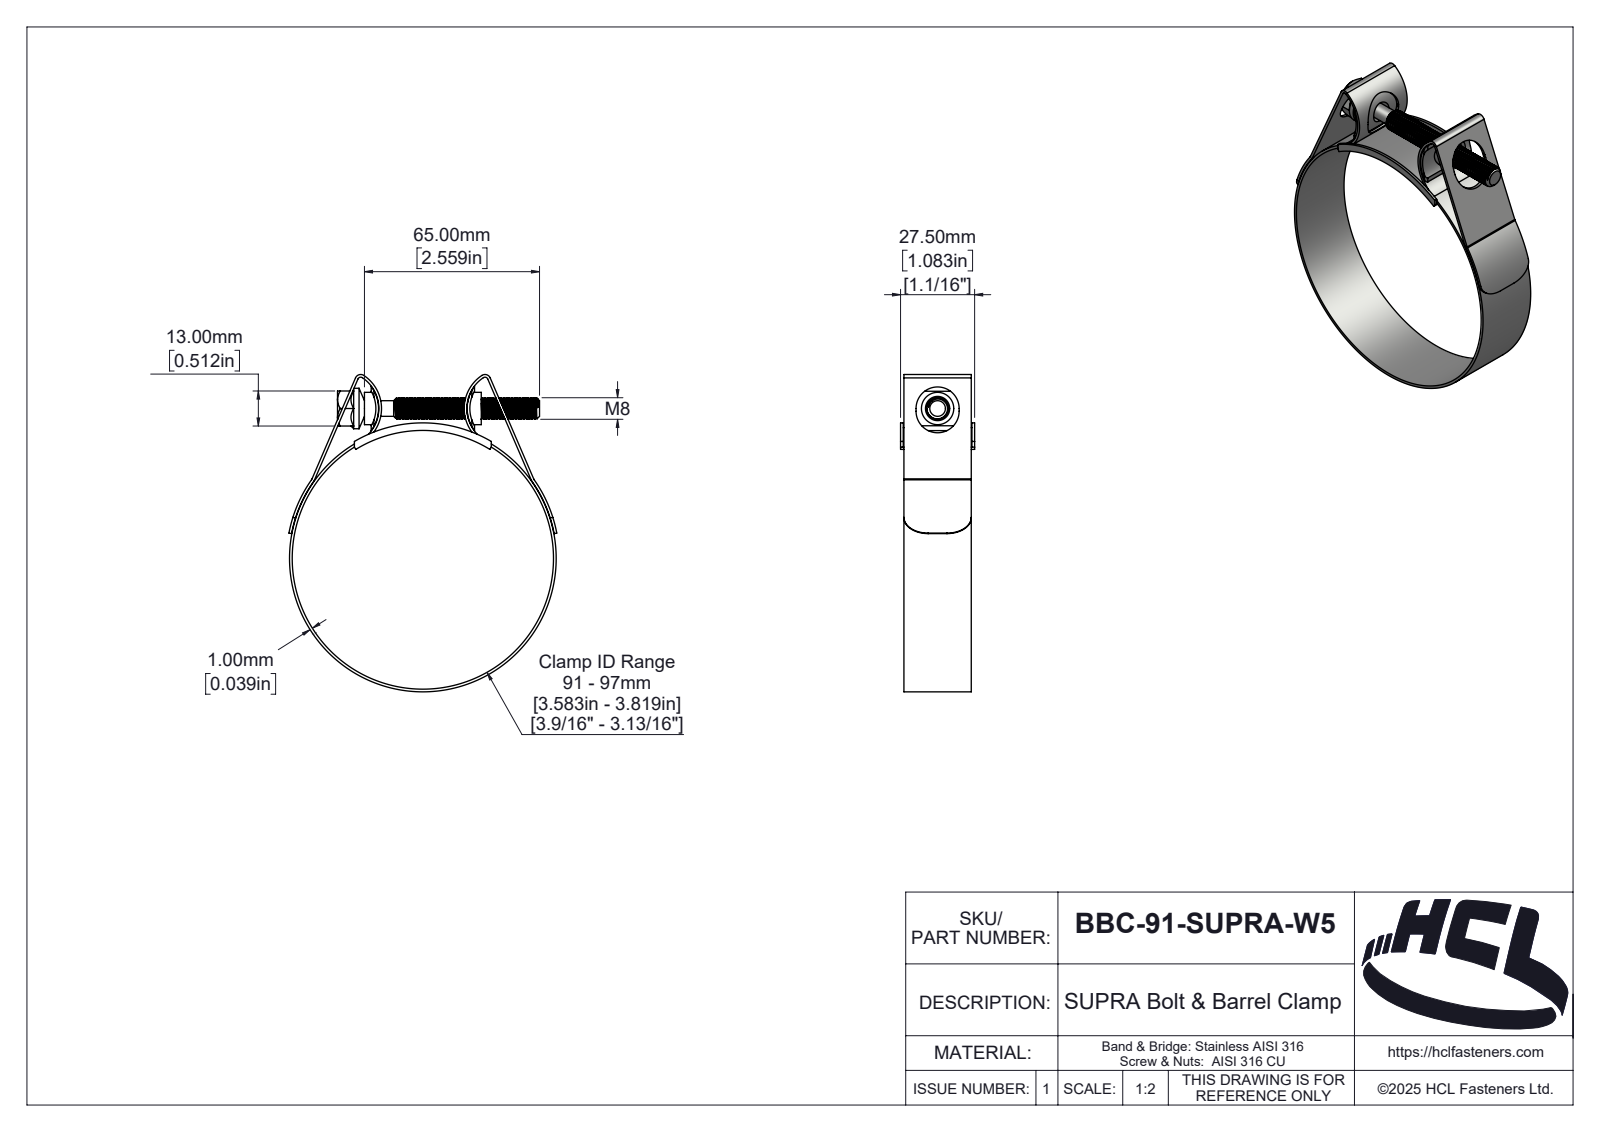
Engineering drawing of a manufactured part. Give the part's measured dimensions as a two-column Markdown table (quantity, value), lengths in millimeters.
| quantity | value |
| --- | --- |
| part name | BBC-91-SUPRA-W5 |
| STEP written by | SolidWorks 2025 (AUTOMOTIVE_DESIGN) |
| units | millimeters |
| bodies | 5 solids, 350 faces (46 planar, 217 cylindrical, 87 other) |
| overall size | 117.75 × 99.44 × 27.5 |
| volume | 17 107 mm³ |
| surface area | 30 127 mm² |
| round holes (diameter × count) | 97 × 1 |
| round bosses / shafts (diameter × count) | 99 × 1, 15.01 × 1, 12 × 1, 8 × 1, 5.8 × 1 |
| partial cylindrical surfaces (radius × count) | 1 × 4, 1.1 × 2, 2 × 2, 2.1 × 2, 3 × 2, 8 × 2, 12.65 × 2, 13.65 × 2 |
| main face-to-face distances | 1, 25, 1.25, 26.25, 26.5, 25.25, 27.5, 13, 2.5, 40.86 |
